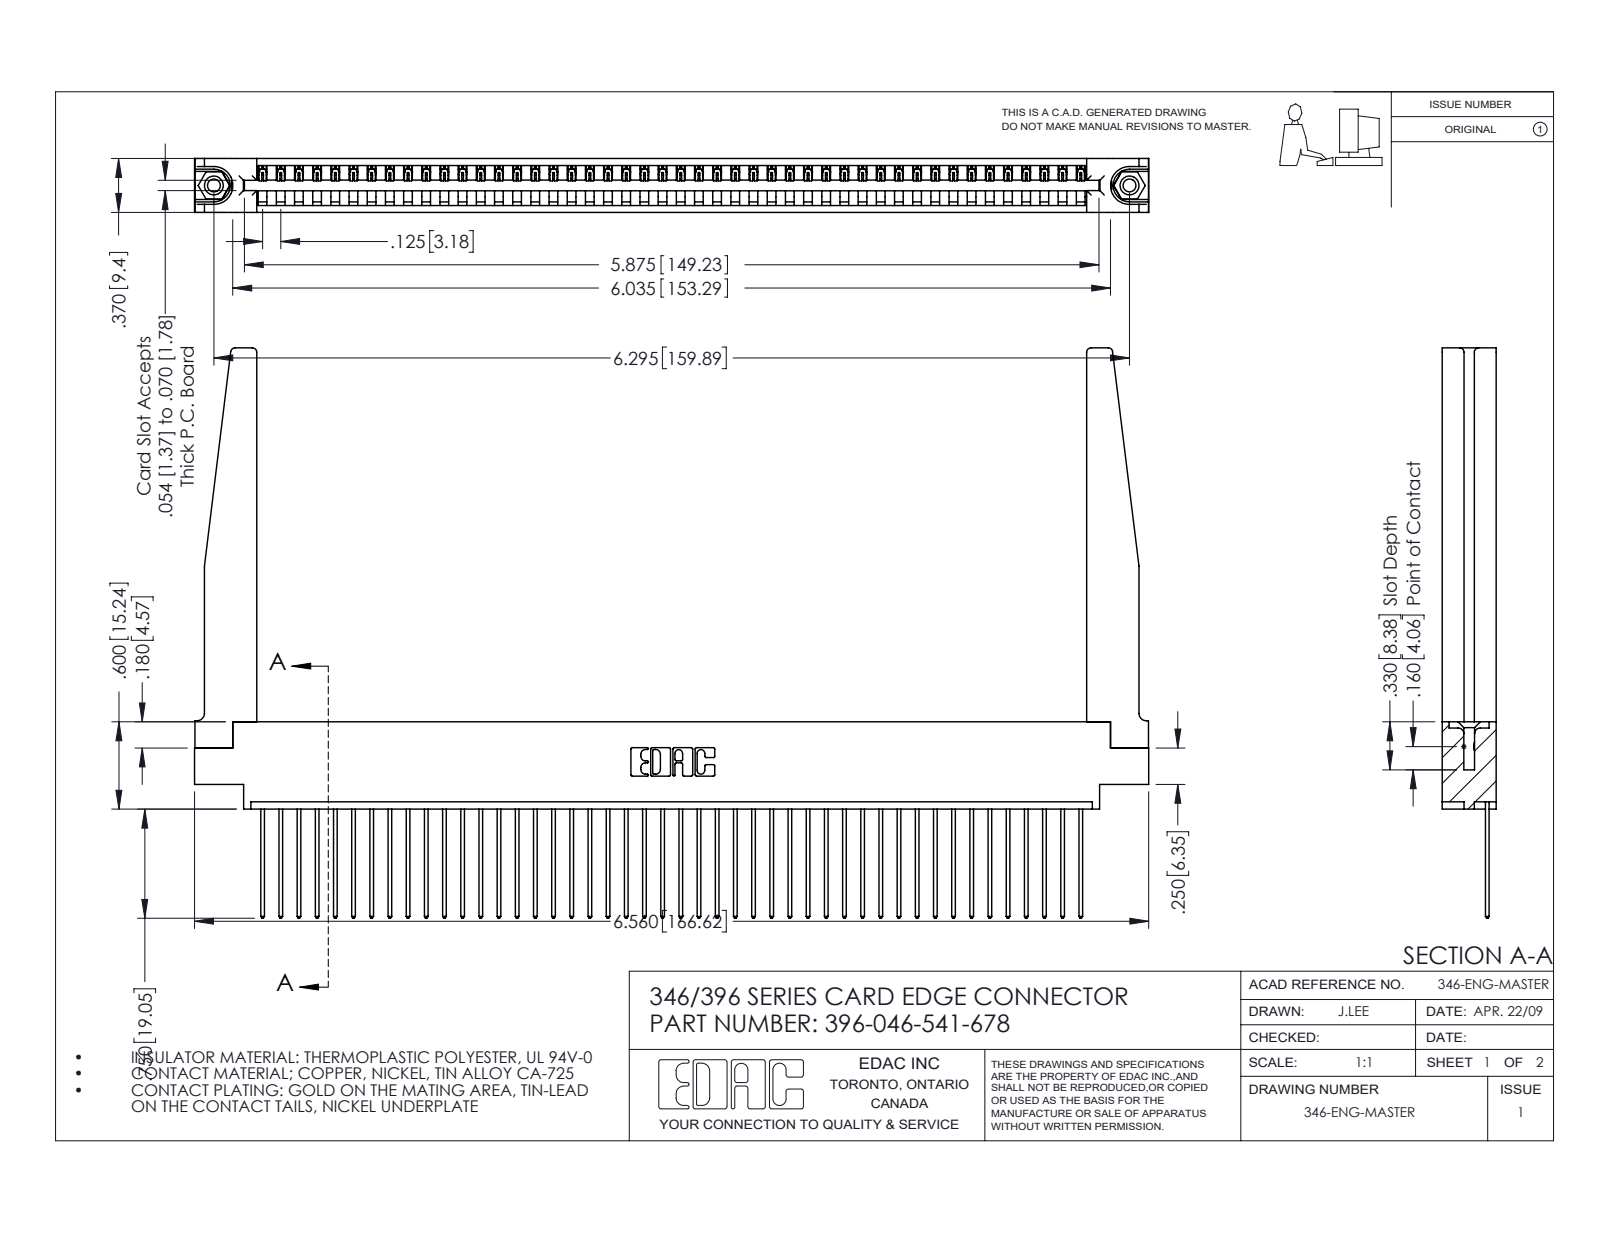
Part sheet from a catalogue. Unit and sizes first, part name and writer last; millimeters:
Units: millimetres
Overall size (bounding box): 166.6 × 99.6 × 9.4
Round holes (diameter × count): ⌀2.3 ×2, ⌀3.2 ×2, ⌀4 ×2, ⌀1.6 ×1
Round bosses / shafts (diameter × count): ⌀3.9 ×2
Partial cylindrical surfaces — rounded edges, fillets, slot ends (radius × count): R0.2 ×92, R0.3 ×92, R0.3 ×22, R0.8 ×8, R0.2 ×6, R0.8 ×6, R0.7 ×3, R0.8 ×2
Main face-to-face distances: 9.4, 1.2, 8.2, 1.8, 6.4, 3.8, 7.6, 0.6, 3.8, 5.6
Hole centre spacings: 6.2, 154.6, 159.9
Volume: 22 880 mm³ · Surface area: 27 620 mm²
Bodies: 51 solids, 3028 faces (2062 planar, 914 cylindrical, 52 other)
Part name (STEP PRODUCT): 346 Part_0.170 Offset - 0.156 Dia-TH; 346-220-078_345-220-078; 396-046-541-678; 345-292-001_345-293-141 (+1 more)
STEP written by: SolidWorks 2016 (CONFIG_CONTROL_DESIGN)
